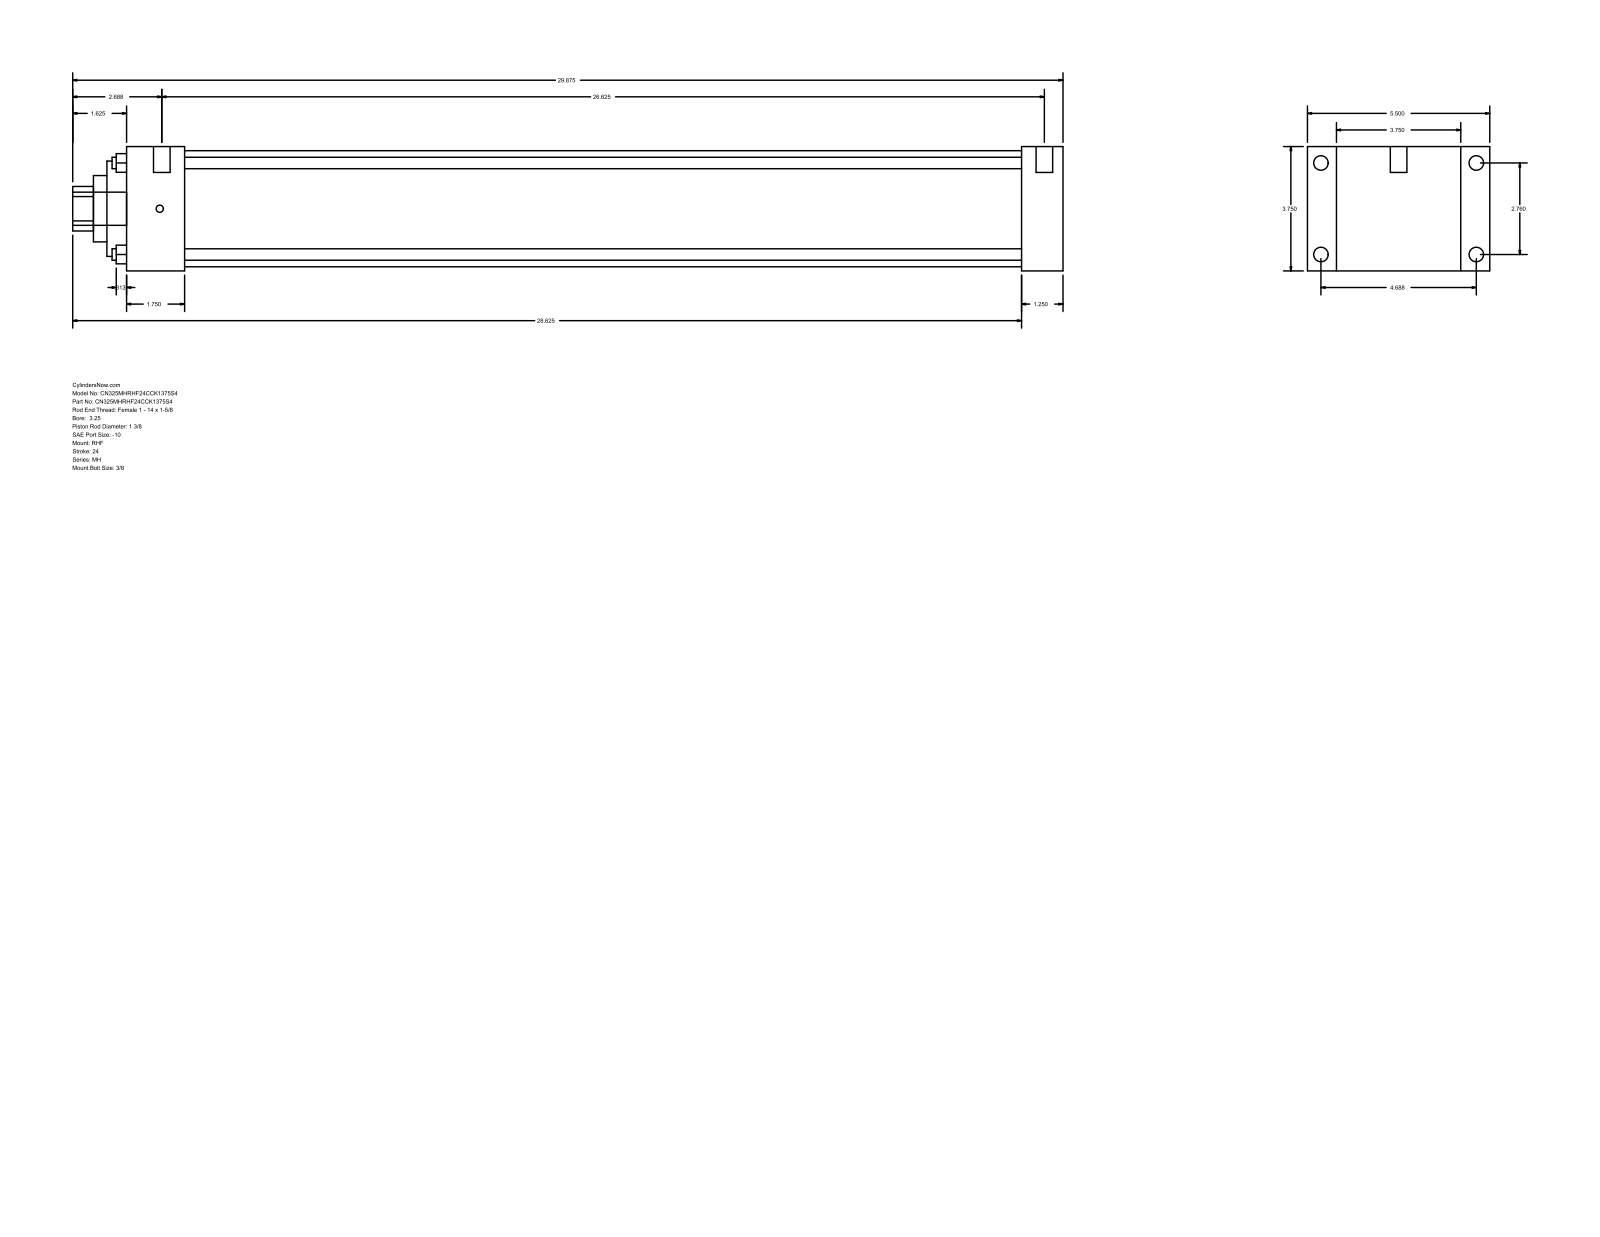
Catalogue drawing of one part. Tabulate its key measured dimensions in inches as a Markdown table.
| quantity | value |
| --- | --- |
| part name | MH_RHF__0325_1.375 |
| STEP written by | GSSL Pune (CONFIG_CONTROL_DESIGN) |
| units | inches |
| bodies | 0 solids, 90 faces (61 planar, 29 cylindrical, 0 other) |
| overall size | 29.875 × 5.5 × 3.75 |
| round holes (diameter × count) | 0.345 × 4, 1.375 × 1, 2 × 1, 2.875 × 1, 3.5 × 1 |
| round bosses / shafts (diameter × count) | 0.438 × 4, 0.219 × 4, 0.5 × 2, 1 × 1 |
| partial cylindrical surfaces (radius × count) | 0.672 × 1 |
| main face-to-face distances | 3.75, 1.25, 0.875, 4.625, 27, 28.25, 5.5, 1.75, 25.25, 26.5 |
| hole center spacings | 1.952, 2.76, 3.903 |
